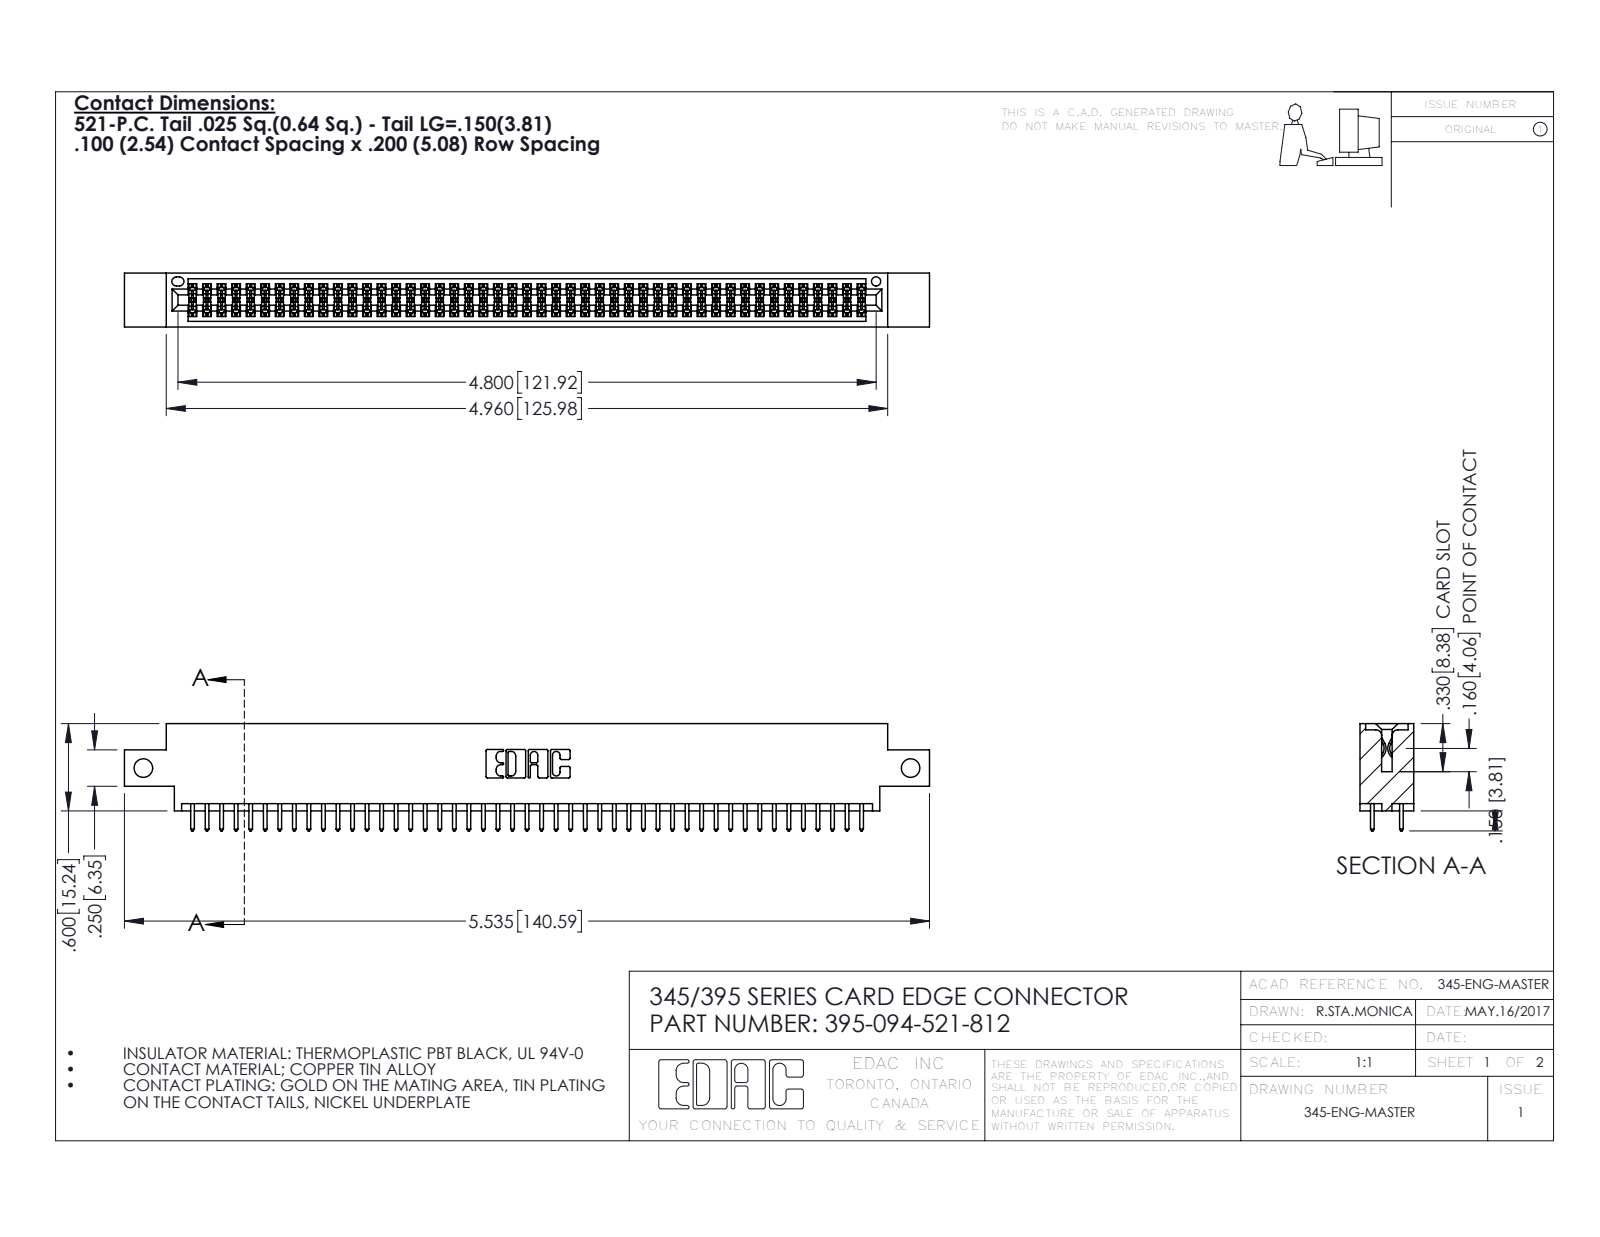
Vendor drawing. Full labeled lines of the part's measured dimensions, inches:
Part name (STEP PRODUCT): 345-292-001_345-293-121; 395-094-521-812; 345 Part_0.170 Offset - Side Mount
STEP written by: SolidWorks 2016 (CONFIG_CONTROL_DESIGN)
Units: inches
Bodies: 95 solids, 4830 faces (3186 planar, 1644 cylindrical, 0 other)
Overall size (bounding box): 5.535 × 0.737 × 0.37
Volume: 0.822 in³ · Surface area: 30.62 in²
Round holes (diameter × count): ⌀0.128 ×2, ⌀0.064 ×1
Partial cylindrical surfaces — rounded edges, fillets, slot ends (radius × count): R0.006 ×141, R0.01 ×94, R0.01 ×22, R0.007 ×6, R0.031 ×6, R0.026 ×3, R0.014 ×2, R0.019 ×2
Main face-to-face distances: 0.298, 0.072, 0.2, 0.37, 0.098, 0.272, 0.025, 0.225, 0.175, 0.149
Hole centre spacings: 5.275
